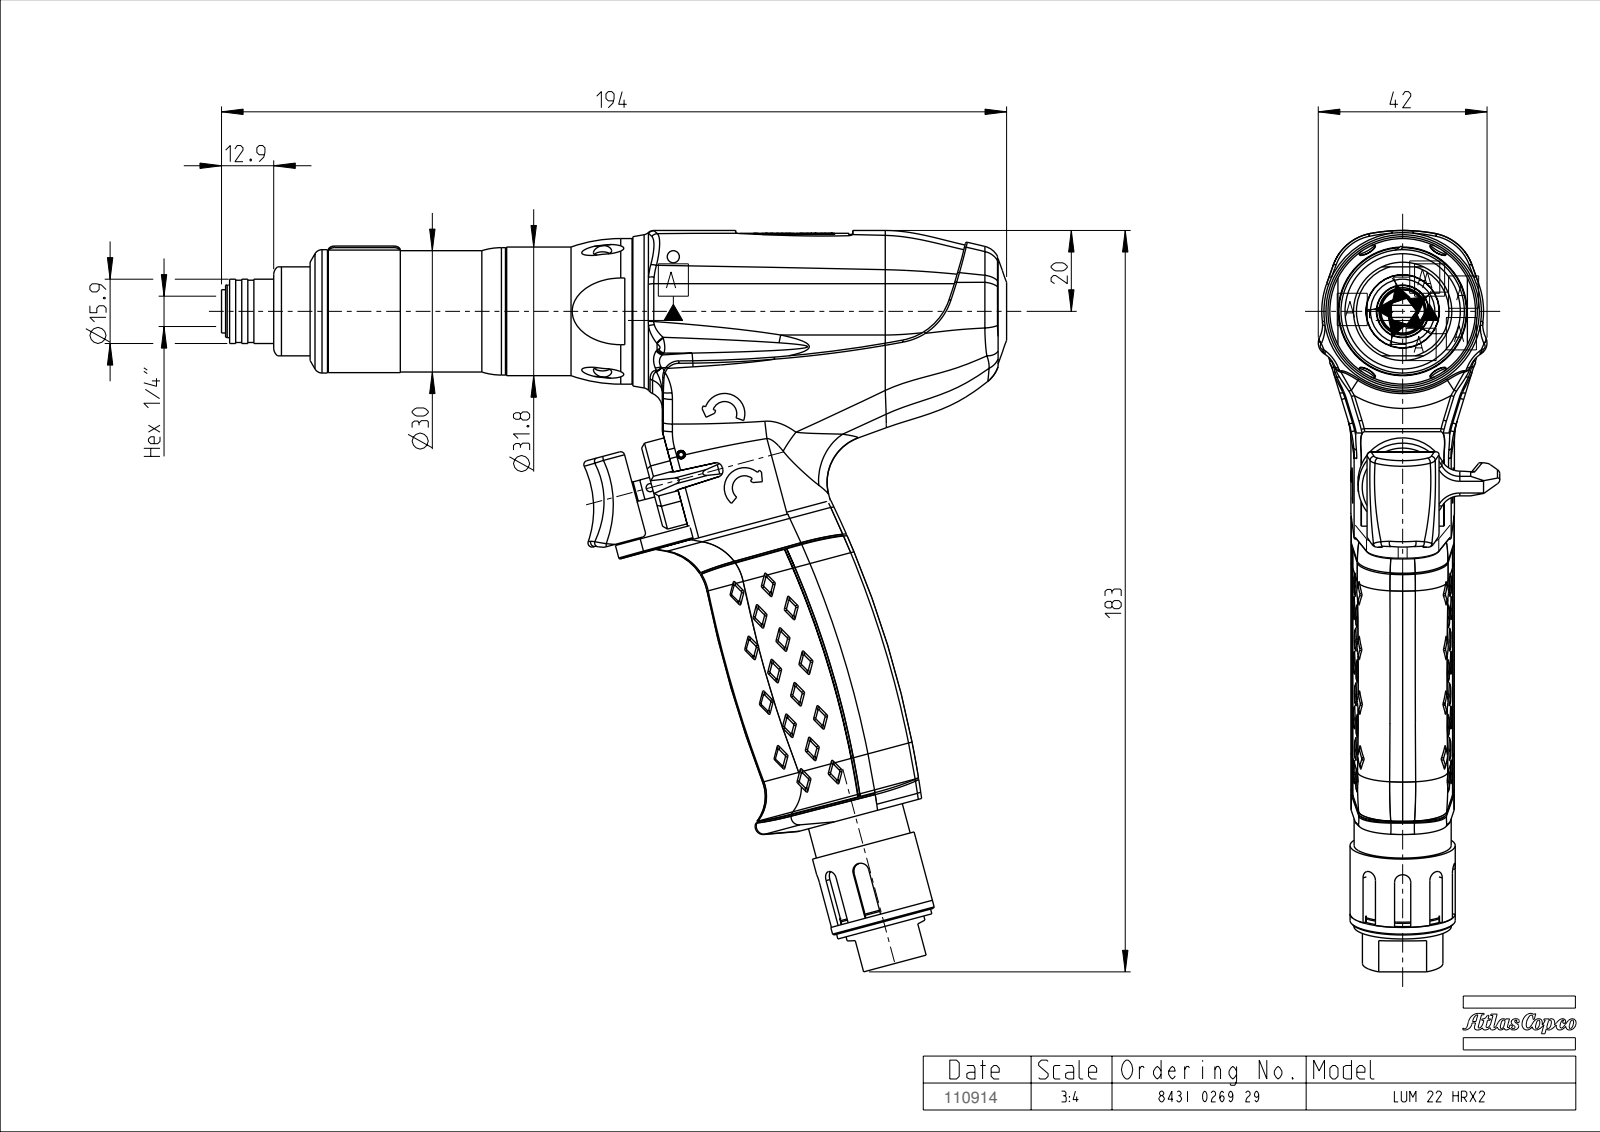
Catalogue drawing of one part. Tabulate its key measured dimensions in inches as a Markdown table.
| quantity | value |
| --- | --- |
| part name | TMP1120_SW |
| STEP written by | PRO/ENGINEER BY PARAMETRIC TECHNOLOGY CORPORATION, 2008310 (CONFIG_CONTROL_DESIGN) |
| units | inches |
| bodies | 0 solids, 817 faces (157 planar, 163 cylindrical, 497 other) |
| overall size | 7.642 × 7.217 × 1.767 |
| round holes (diameter × count) | 0.177 × 2, 0.118 × 1, 0.295 × 1, 0.451 × 1 |
| round bosses / shafts (diameter × count) | 1.417 × 1, 1.252 × 1, 1.24 × 1, 1.201 × 1, 1.193 × 1, 1.181 × 1, 1.024 × 1, 0.949 × 1 |
| partial cylindrical surfaces (radius × count) | 0.039 × 16, 0.098 × 5, 0.02 × 4, 0.059 × 4, 0.079 × 4, 0.13 × 4, 0.157 × 3, 0.197 × 3 |
| main face-to-face distances | 0.031, 0.25, 0.059, 3.15, 0.236, 0.236, 0.768, 1.063, 4.213, 4.256 |
